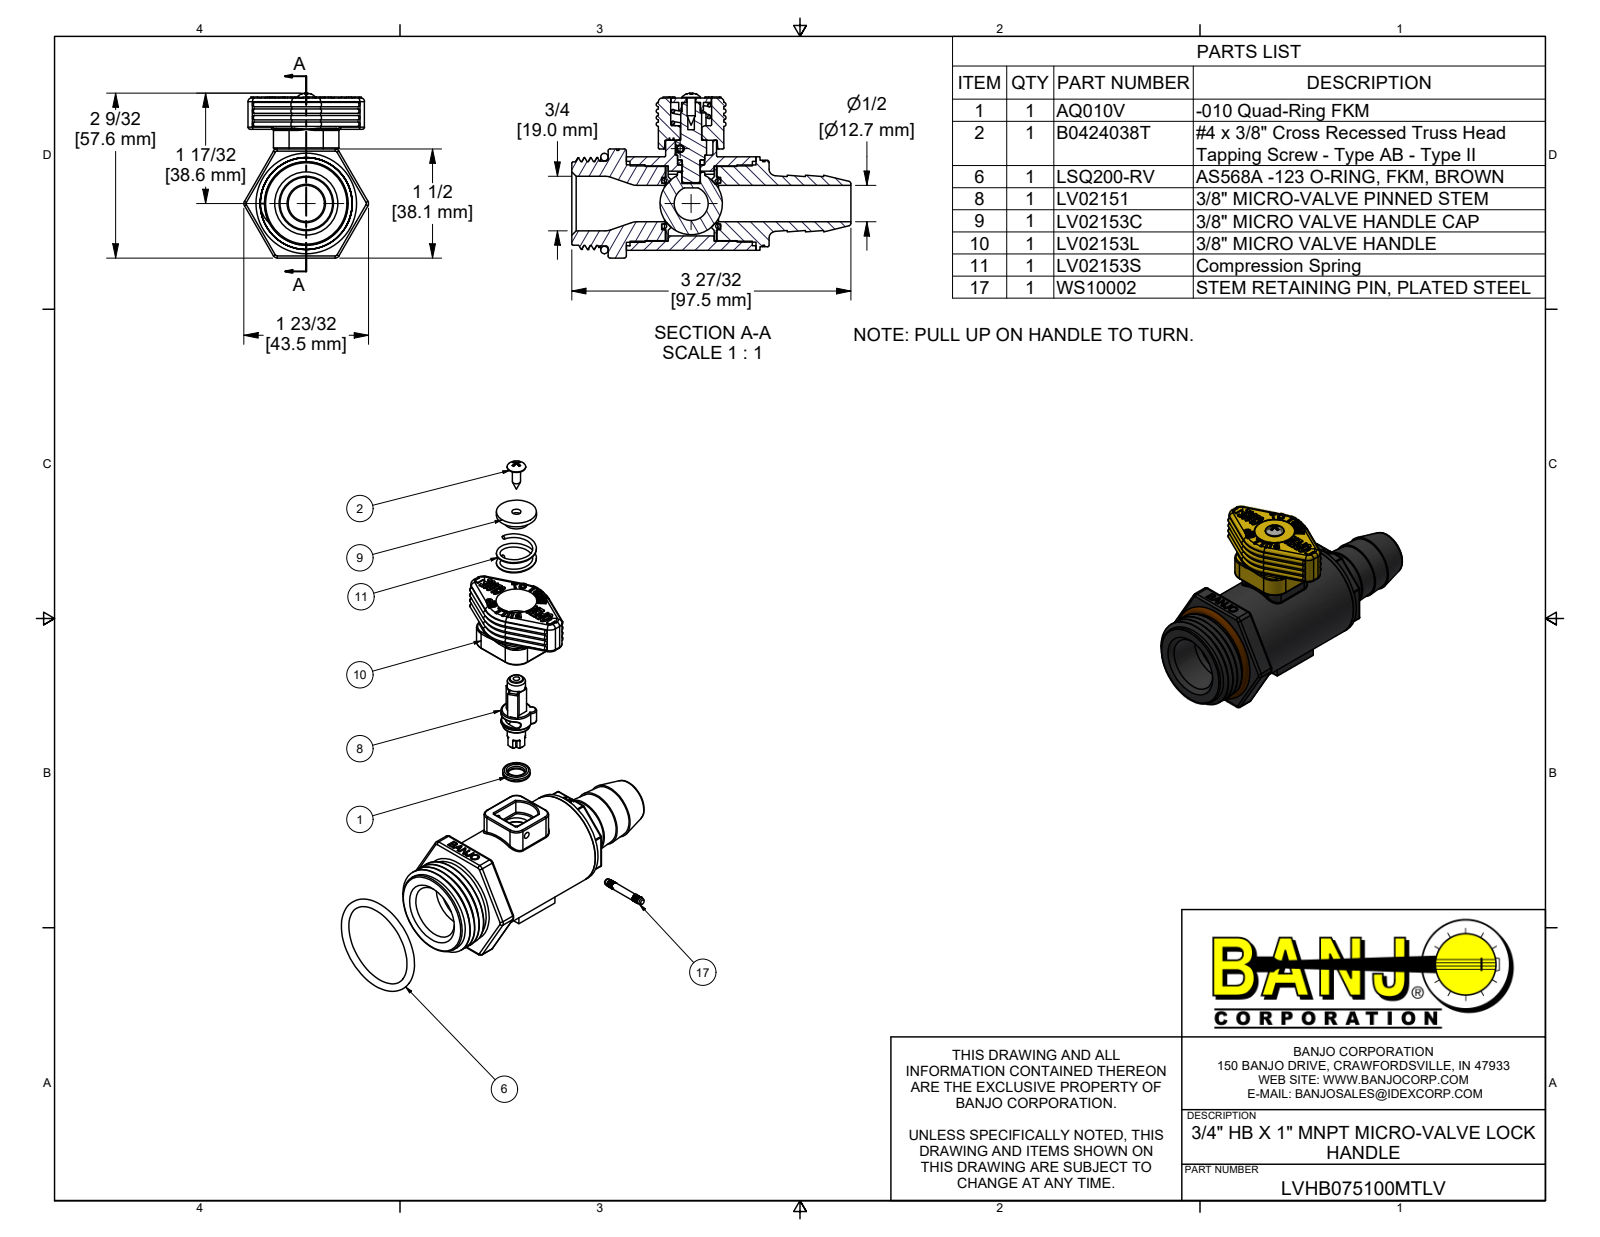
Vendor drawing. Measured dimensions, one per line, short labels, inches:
name: LVHB075100MTLV; LV05254A; LVHB07256A; LVHB07256 (+8 more)
written by: Autodesk Inventor 2022 (AUTOMOTIVE_DESIGN)
unit: in
bodies: 17 solids, 2289 faces (1580 planar, 222 cylindrical, 487 other)
size: 3.837 × 2.269 × 1.714
volume: 3.697 in³; area: 56.16 in²
holes: 1× ⌀0.089, 1× ⌀0.093, 1× ⌀0.125, 1× ⌀0.251, 1× ⌀0.26, 1× ⌀0.366, 1× ⌀0.376, 1× ⌀0.47, 1× ⌀0.5, 1× ⌀0.541, 1× ⌀0.562, 1× ⌀0.718
bosses: 1× ⌀1.285, 1× ⌀1.165, 1× ⌀1.064, 1× ⌀1.062, 1× ⌀1.024, 1× ⌀1.02, 1× ⌀0.558, 1× ⌀0.552
rounds: 52× R0.03, 36× R0.015, 16× R0.01, 16× R0.02, 8× R0.05, 6× R0.06, 4× R0.109, 4× R0.125
face distances: 1.207, 0.05, 0.575, 1.247, 0.04, 0.03, 0.545, 1.237, 0.662, 0.535
hole spacings: 0.769
